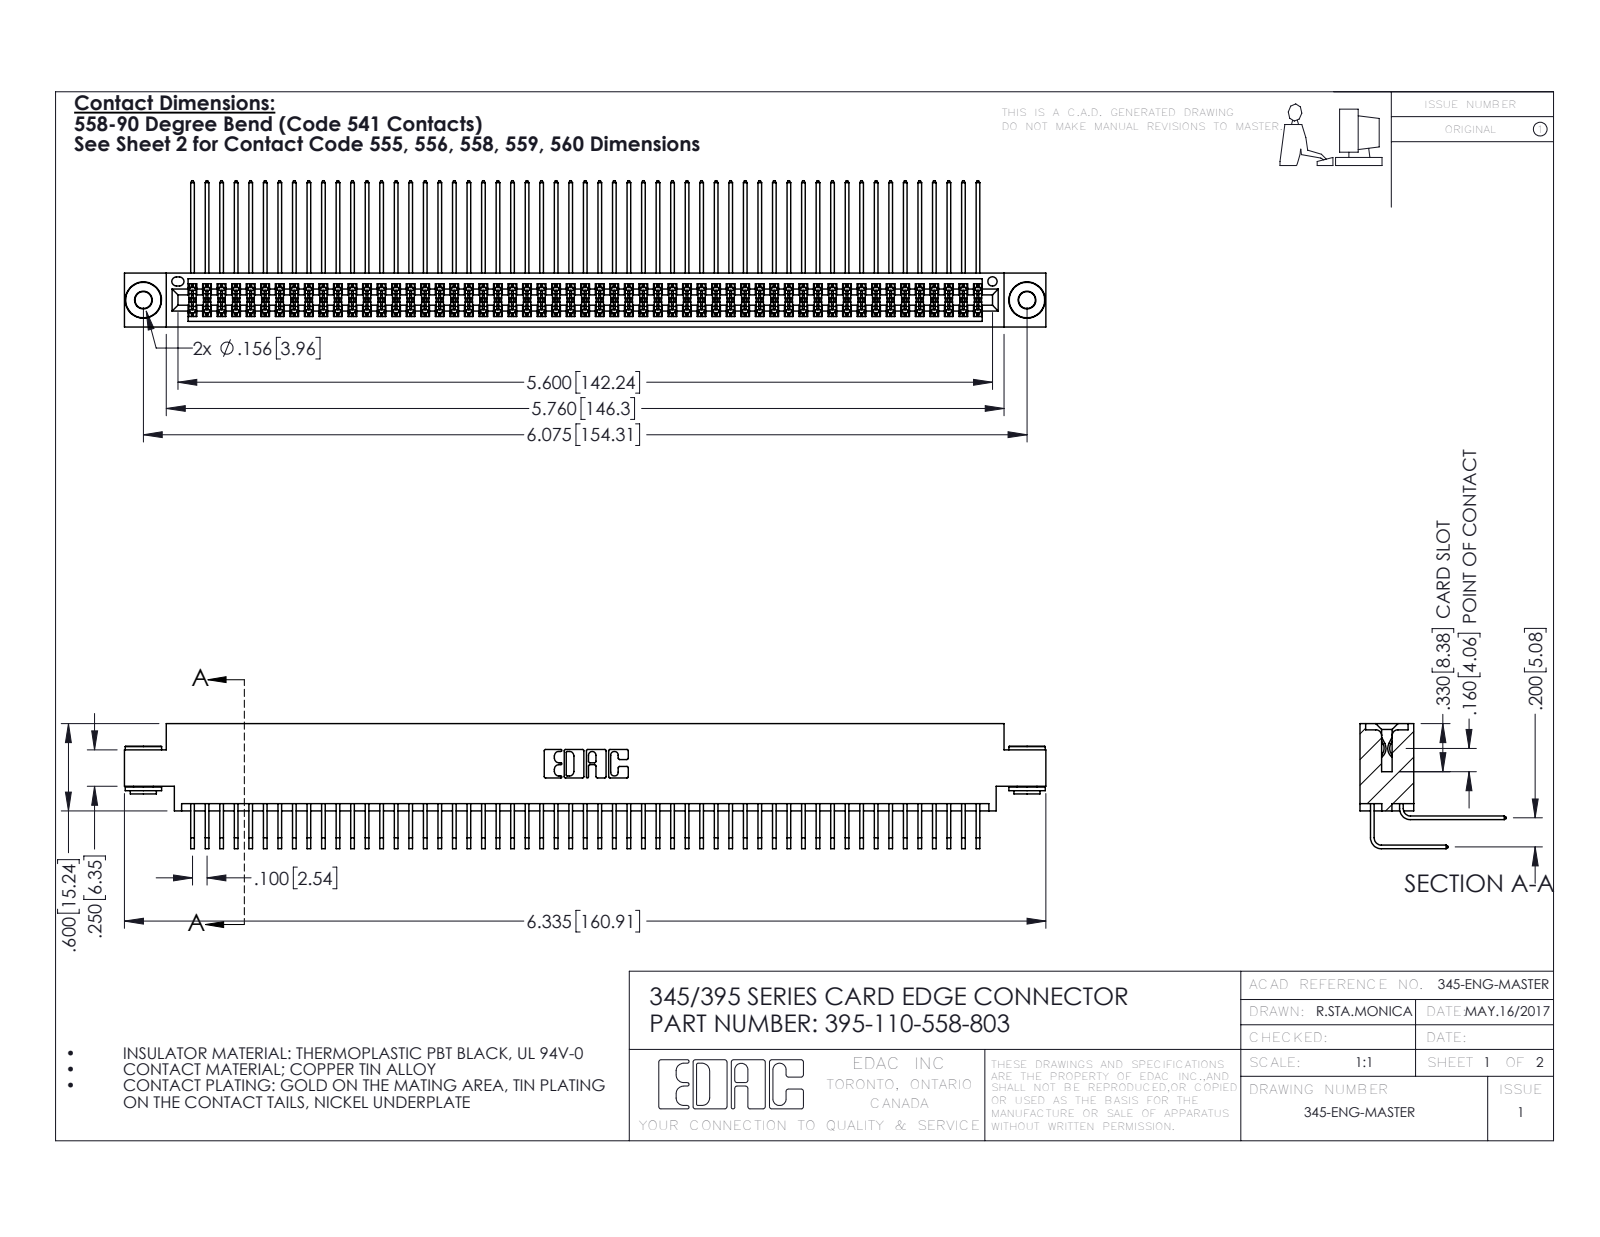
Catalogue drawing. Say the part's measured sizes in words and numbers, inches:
The part is named "345-292-001_558 559 Tail - 1; 345 Part_0.170 Offset - 0.156 Dia-TH; 395-110-558-803; 345-250-002_345-250-002-102 (+1 more)". Its 3-D file was written by "SolidWorks 2016 (CONFIG_CONTROL_DESIGN)". It is 113 solids with 5888 faces: 3944 planar, 1936 cylindrical and 8 other. Overall it measures 6.335 by 1.005 by 0.859 inches. Its volume is 0.994 cubic inches and its surface area 42.88 square inches. Round holes: 2 of diameter 0.116, 2 of diameter 0.156, 1 of diameter 0.064. Round bosses or shafts: 2 of diameter 0.25, 2 of diameter 0.18, 2 of diameter 0.136. Partial cylindrical surfaces (rounded edges, fillets, slot ends): 165 of radius 0.006, 22 of radius 0.01, 6 of radius 0.007, 6 of radius 0.031, 3 of radius 0.026, 2 of radius 0.014, 2 of radius 0.019, 2 of radius 0.022. The main face-to-face distances are 0.072, 0.298, 0.2, 0.37, 0.098, 0.272, 0.025, 0.225, 0.175, 0.025. The hole center spacings are 0.27, 5.839, 6.075.
